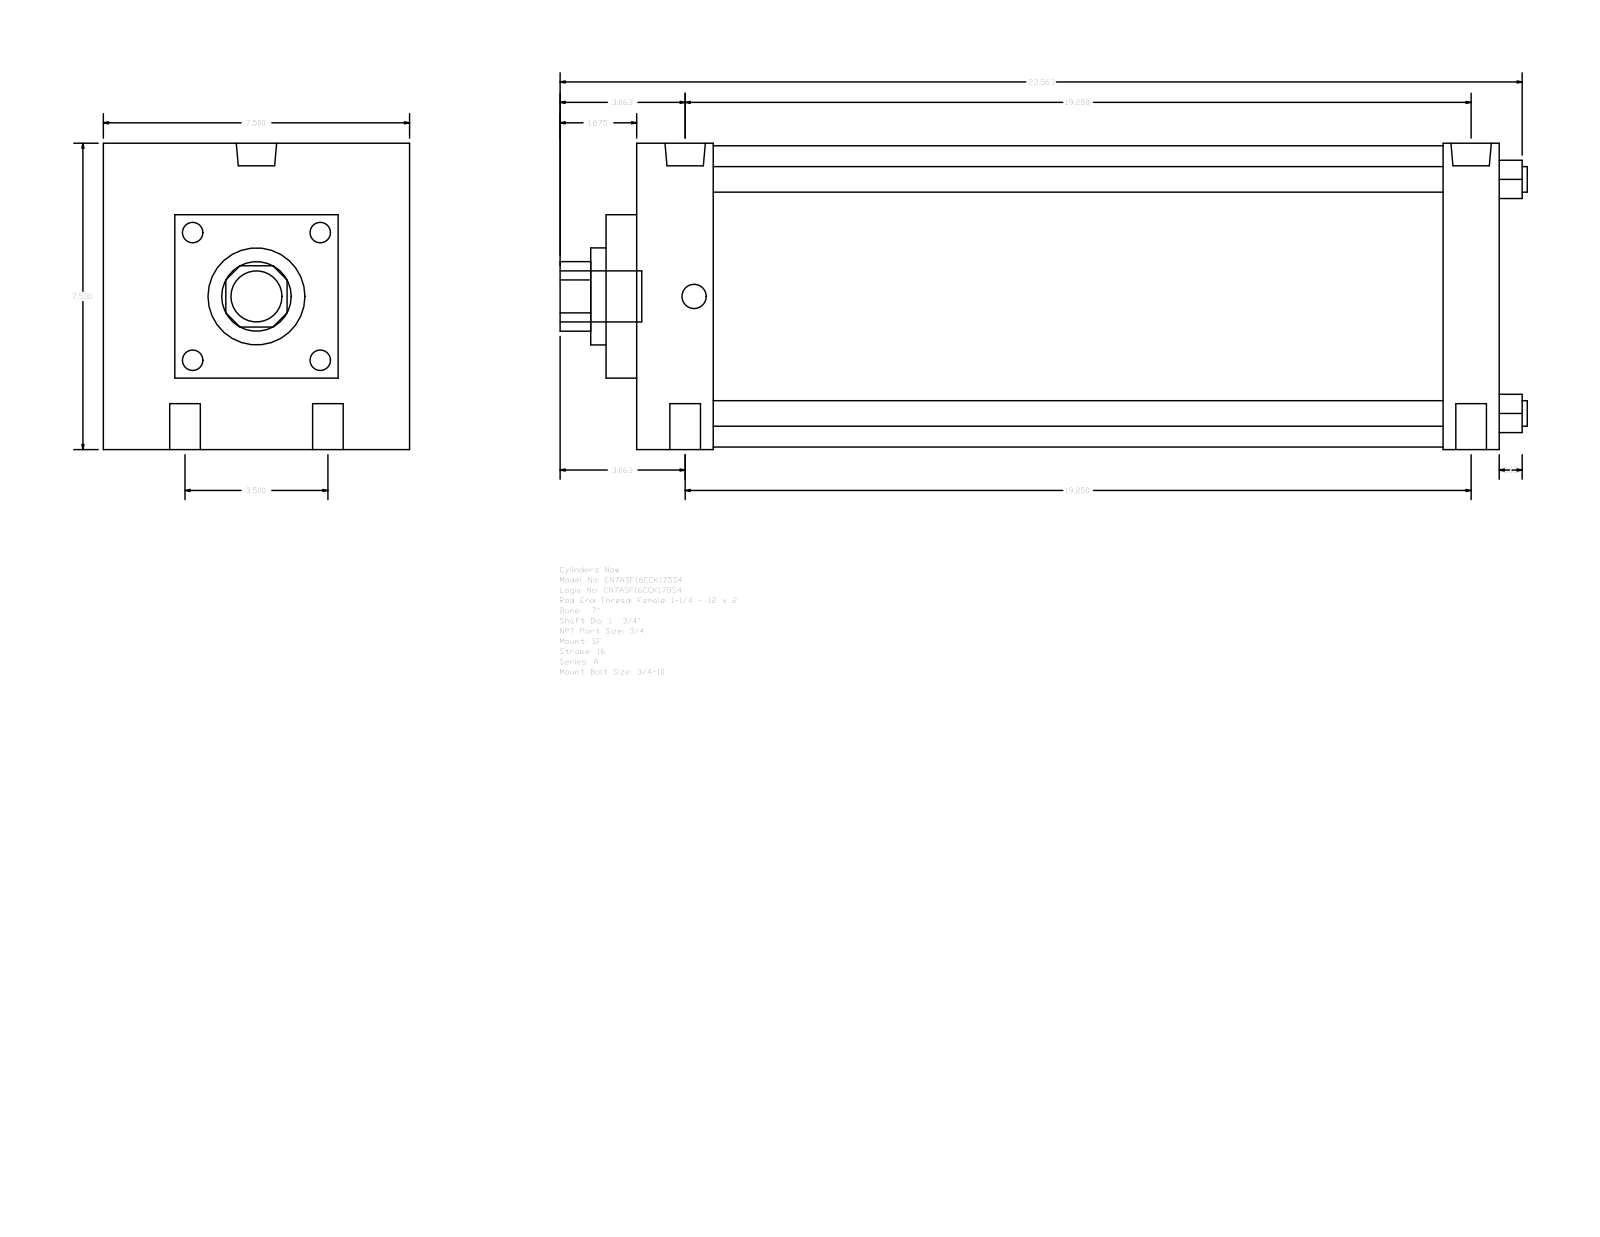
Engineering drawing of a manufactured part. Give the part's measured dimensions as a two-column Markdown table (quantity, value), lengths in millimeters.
| quantity | value |
| --- | --- |
| part name | A_SF__0700_1.75 |
| STEP written by | GSSL Pune (CONFIG_CONTROL_DESIGN) |
| units | millimeters |
| bodies | 0 solids, 93 faces (67 planar, 26 cylindrical, 0 other) |
| overall size | 601.66 × 190.5 × 190.5 |
| round holes (diameter × count) | 19.05 × 4, 15.08 × 2, 25.12 × 2, 44.45 × 1, 60.33 × 1 |
| round bosses / shafts (diameter × count) | 15.88 × 4, 187.32 × 1, 31.75 × 1 |
| partial cylindrical surfaces (radius × count) | 21.63 × 1 |
| main face-to-face distances | 190.5, 536.58, 44.45, 19.05, 47.63, 501.65, 454.02, 488.95, 34.93, 146.05 |
| hole center spacings | 44.45, 490.97, 488.95, 88.9, 496.97, 477.83 |
